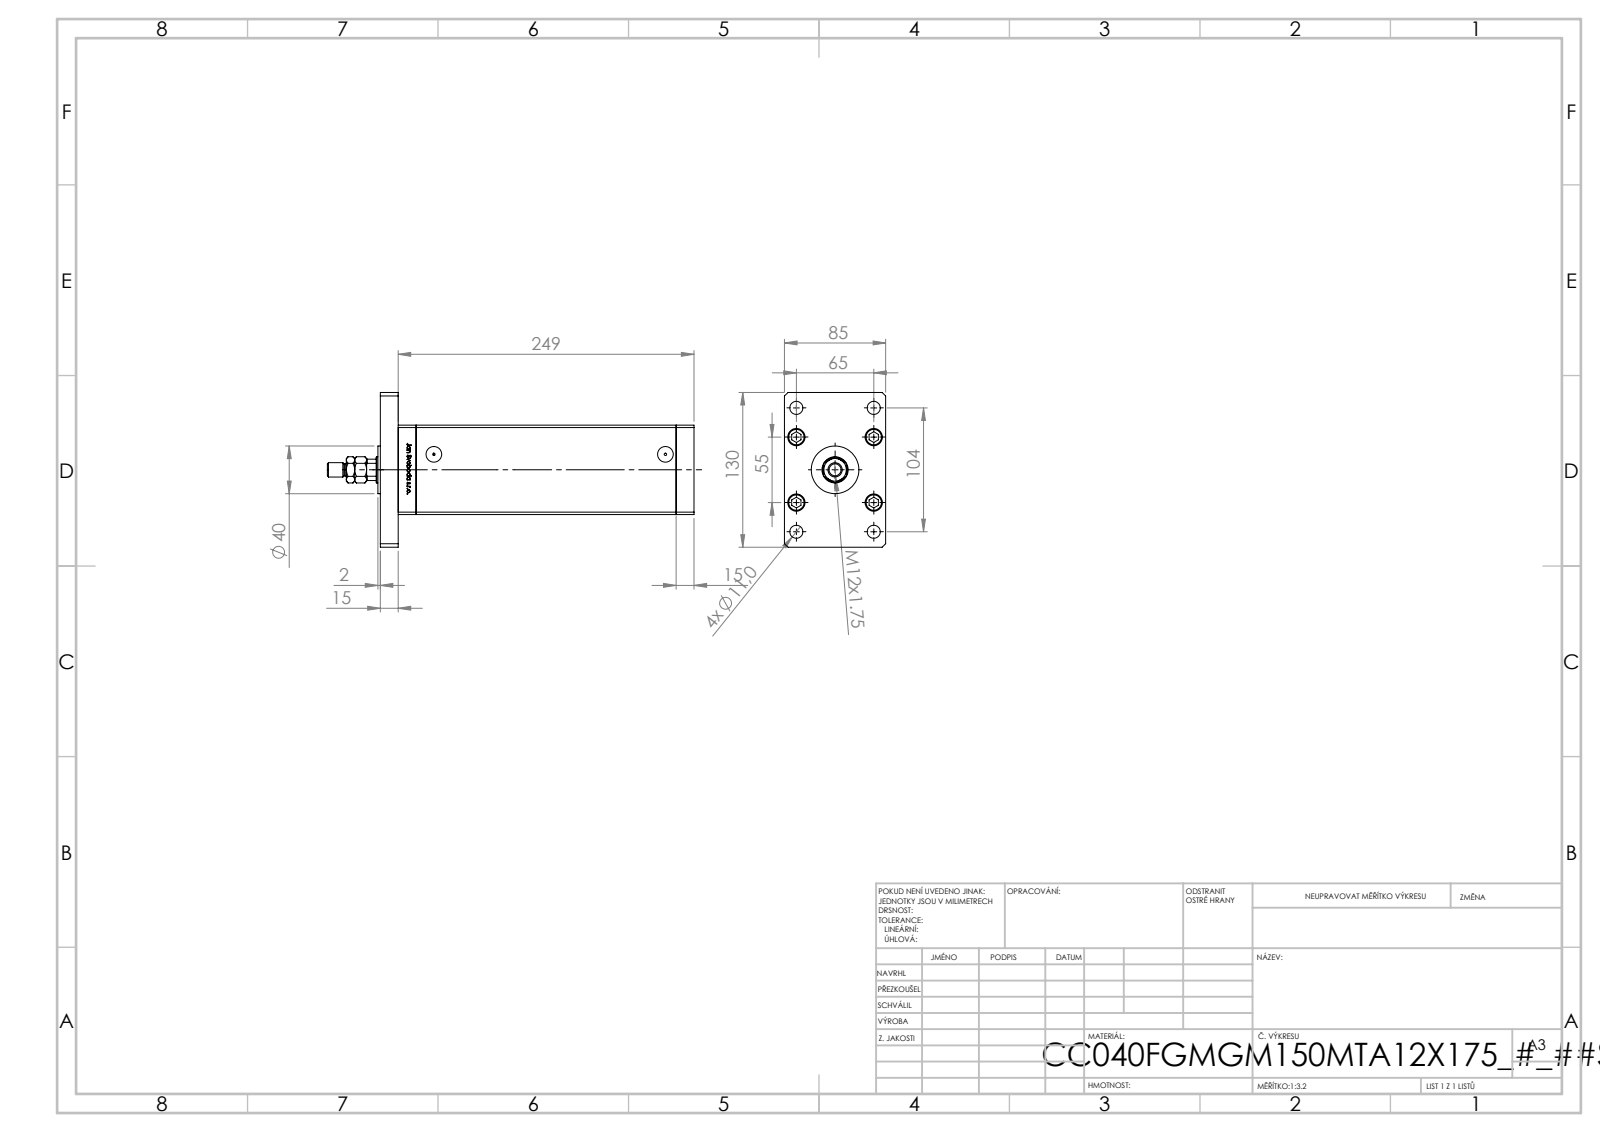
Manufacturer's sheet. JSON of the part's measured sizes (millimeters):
{"part_name": "V220C_F; ALLEN BOLT; V220C_F_MIDDLE; V220C_VC_F (+3 more)", "step_written_by": "SolidWorks 2019 (CONFIG_CONTROL_DESIGN)", "units": "millimeters", "bodies": {"solids": 20, "faces": 1357, "planar": 530, "cylindrical": 191, "other": 636}, "overall_size": [308, 130, 85], "volume_mm3": 1543000, "surface_area_mm2": 238574, "round_holes": [[11, 9], [15.5, 5], [10, 4], [14.5, 4], [2, 2], [13.16, 2], [13.5, 1], [22, 1], [23.5, 1]], "round_bosses_or_shafts": [[8, 9], [14.5, 5], [40, 1], [12, 1], [10, 1]], "partial_cylinders_radius": [[0.93, 2], [10.5, 1]], "face_to_face_distances": [15, 85, 75, 233.5, 248.5, 218.5, 30, 263.5, 10.5, 27.5], "hole_center_spacings": [28, 24.5, 42.57, 61.32, 65, 69.46, 79.5, 102.69]}
